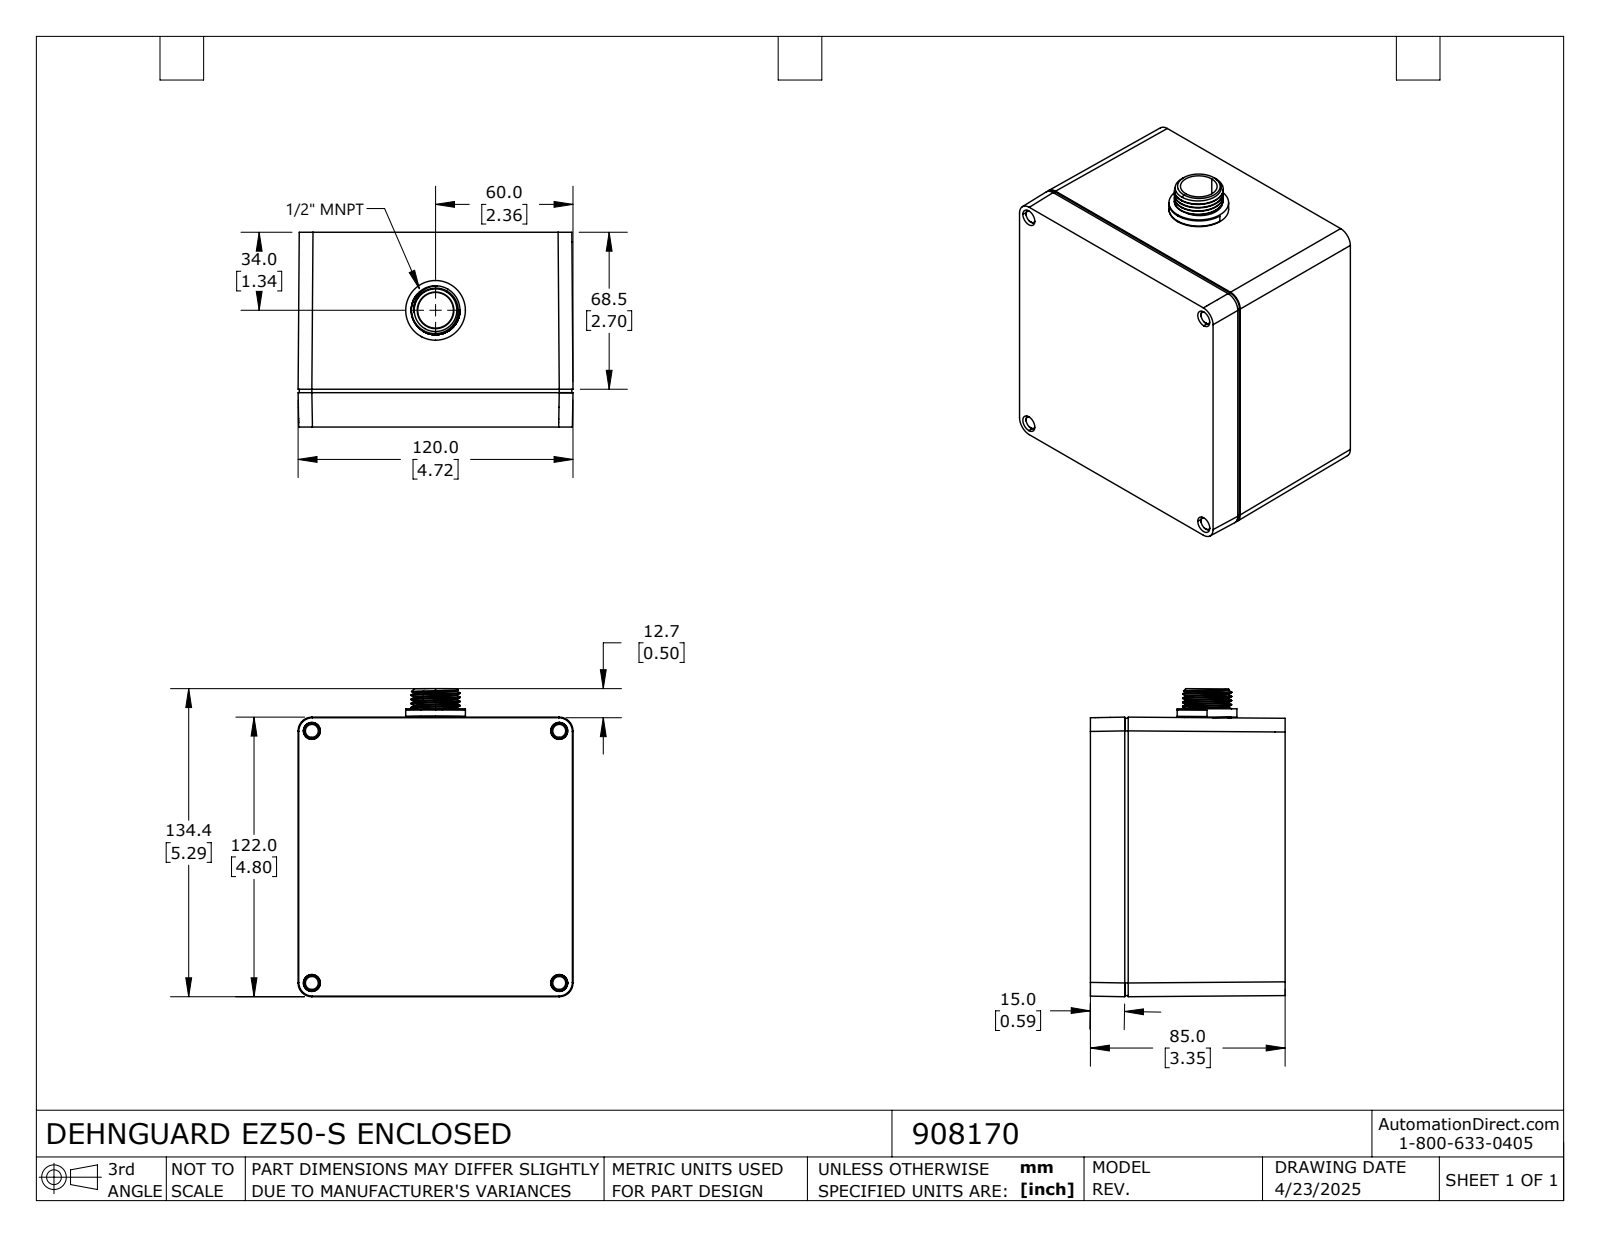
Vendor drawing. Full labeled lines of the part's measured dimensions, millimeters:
Part name (STEP PRODUCT): 908170
STEP written by: SolidWorks 2024 (AUTOMOTIVE_DESIGN)
Units: millimetres
Bodies: 2 solids, 836 faces (588 planar, 173 cylindrical, 75 other)
Overall size (bounding box): 134.4 × 120 × 85
Volume: 538 300 mm³ · Surface area: 190 500 mm²
Round holes (diameter × count): ⌀4.2 ×4, ⌀8 ×4
Round bosses / shafts (diameter × count): ⌀7 ×6, ⌀2.9 ×4, ⌀29.6 ×1, ⌀28.6 ×1, ⌀26.1 ×1, ⌀21.3 ×1
Partial cylindrical surfaces — rounded edges, fillets, slot ends (radius × count): R0.1 ×12, R1.2 ×12, R6 ×8, R5.5 ×4, R0.5 ×3, R0.2 ×2, R0.4 ×2, R0.8 ×2
Main face-to-face distances: 3, 4, 85, 81, 82, 78, 3, 1, 9.4, 3
Hole centre spacings: 90, 110, 142.1
